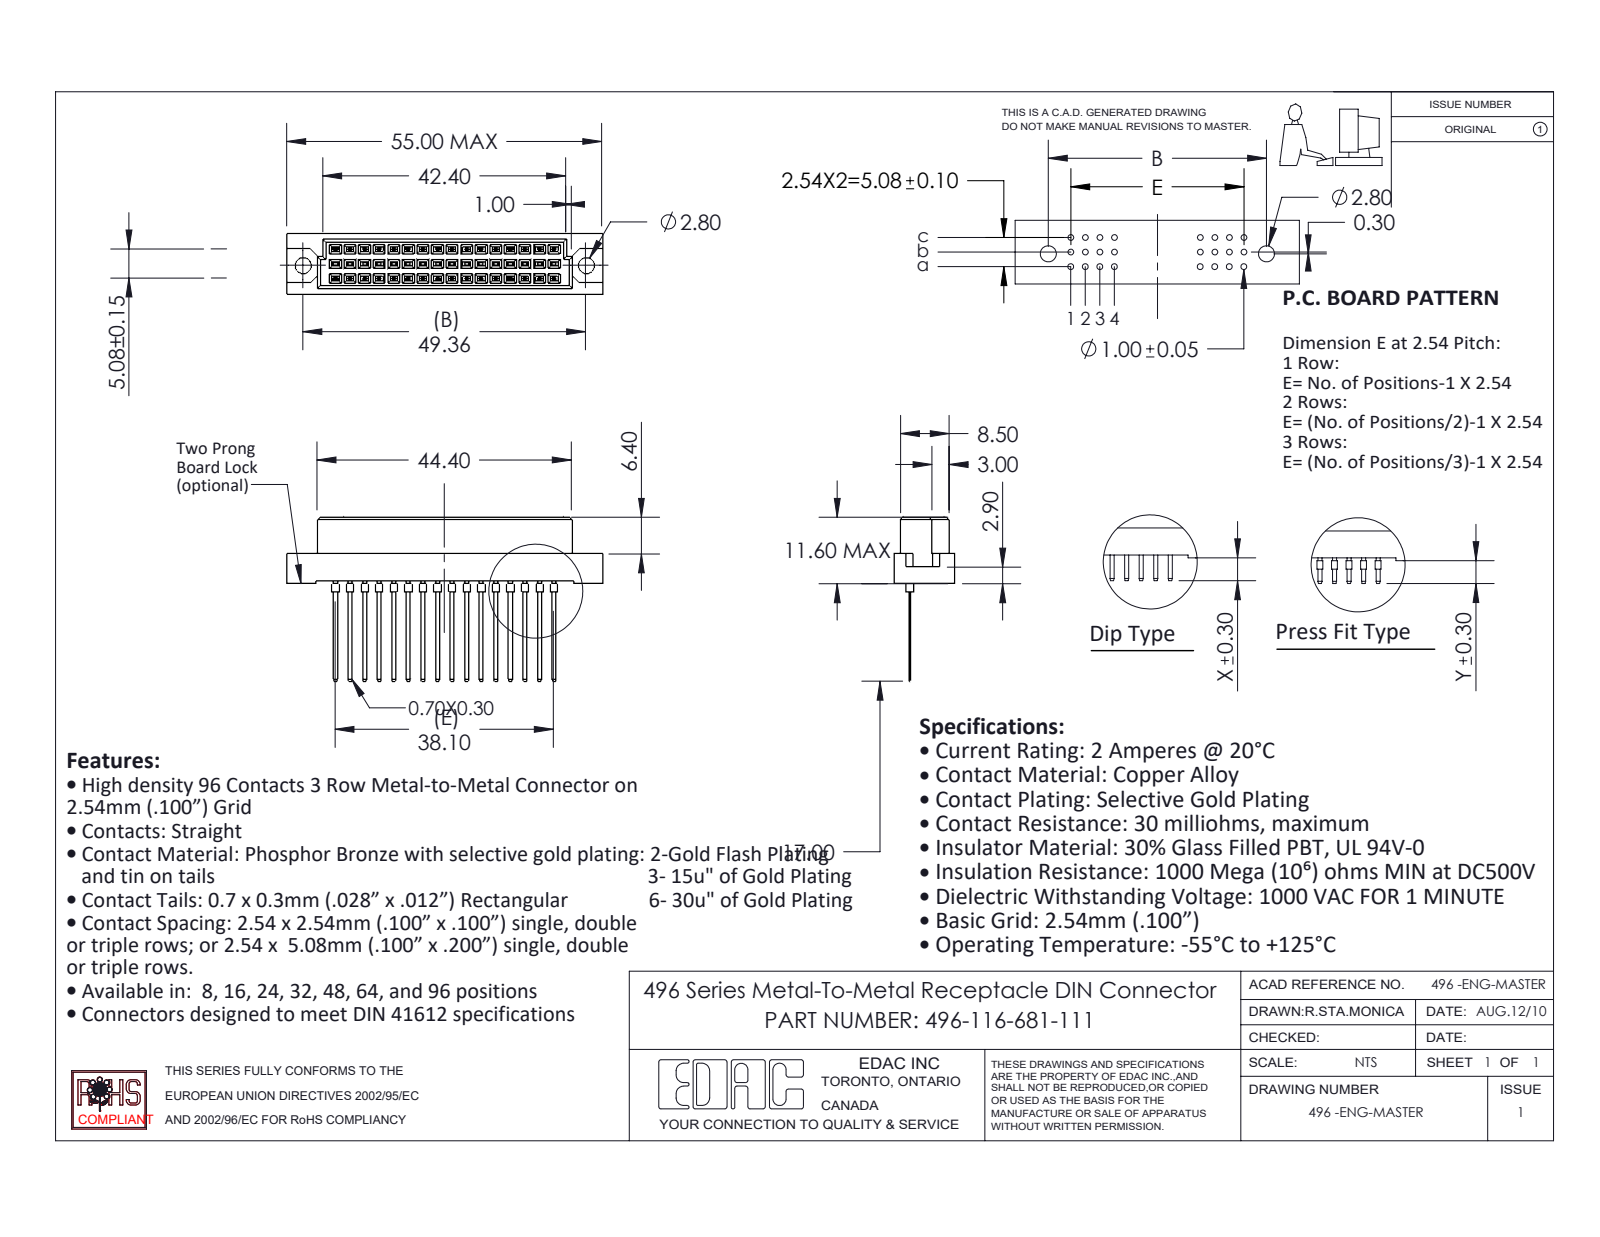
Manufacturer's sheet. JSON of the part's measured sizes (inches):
{"part_name": "496 Part_48; 496-116-681-111; 496-290_81", "step_written_by": "SolidWorks 2020 (CONFIG_CONTROL_DESIGN)", "units": "inches", "bodies": {"solids": 17, "faces": 954, "planar": 918, "cylindrical": 36, "other": 0}, "overall_size": [2.165, 1.126, 0.417], "volume_in3": 0.285, "surface_area_in2": 7.671, "round_holes": [[0.11, 2]], "round_bosses_or_shafts": [[0.039, 16]], "face_to_face_distances": [0.1, 0.2, 0.041, 0.376, 0.032, 0.115, 0.303, 0.103, 0.315, 0.073], "hole_center_spacings": [1.943]}
